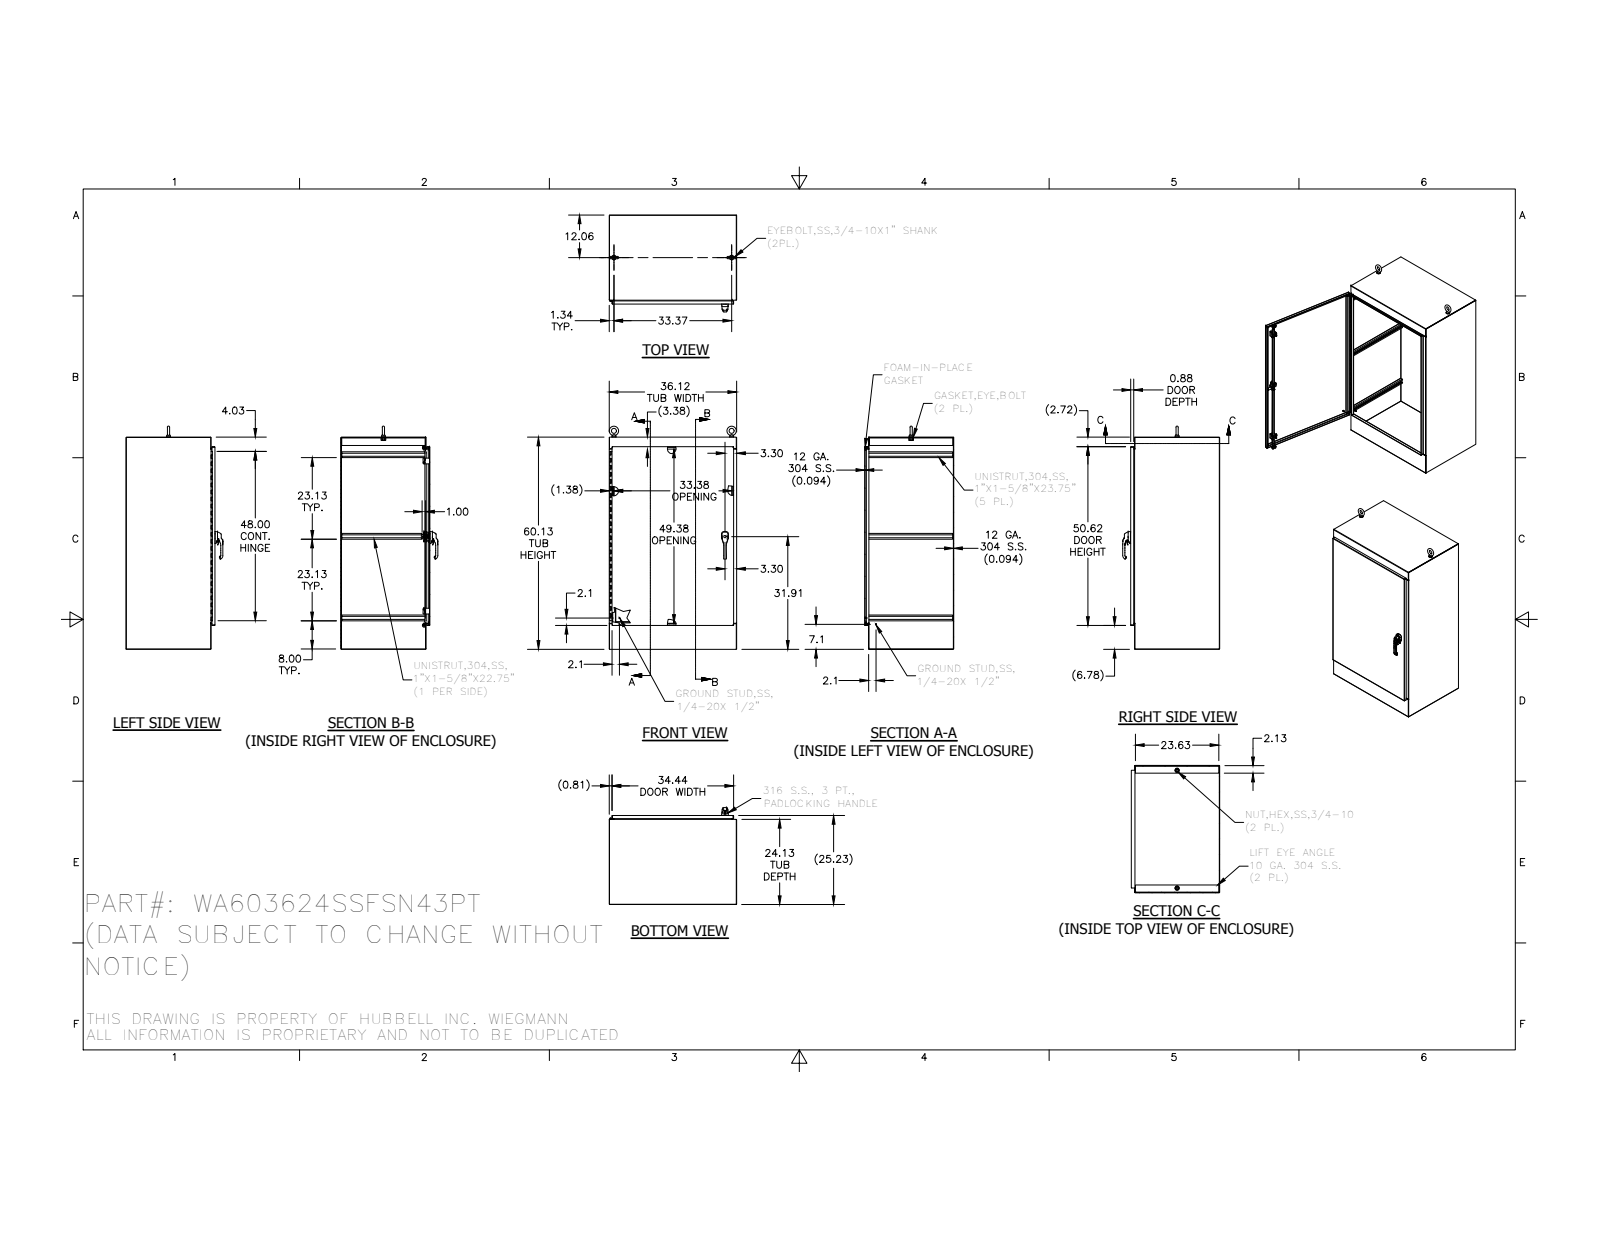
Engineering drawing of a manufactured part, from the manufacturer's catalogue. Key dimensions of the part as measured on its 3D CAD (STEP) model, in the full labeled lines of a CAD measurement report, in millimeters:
Part name (STEP PRODUCT): HFW369101; 37028; FUN00132_23.75(_DQ); 1091-BR11_AF0 (+8 more)
STEP written by: SolidWorks 2014 (AUTOMOTIVE_DESIGN)
Units: millimetres
Bodies: 66 solids, 3391 faces (1174 planar, 1277 cylindrical, 940 other)
Overall size (bounding box): 1606.5 × 917.6 × 697.9
Volume: 16 880 000 mm³ · Surface area: 13 730 000 mm²
Round holes (diameter × count): ⌀6.7 ×8, ⌀9.5 ×8, ⌀4.7 ×4, ⌀5.4 ×3, ⌀6.4 ×3, ⌀7.1 ×3, ⌀4.2 ×2, ⌀6.1 ×2, ⌀6.4 ×2, ⌀8 ×2, ⌀10.2 ×2, ⌀10.2 ×2
Round bosses / shafts (diameter × count): ⌀25.4 ×3, ⌀6 ×3, ⌀31.8 ×2, ⌀28.4 ×2, ⌀19.1 ×2, ⌀14.3 ×2, ⌀13.5 ×2, ⌀13.5 ×2
Partial cylindrical surfaces — rounded edges, fillets, slot ends (radius × count): R0.5 ×178, R0.3 ×106, R3.2 ×26, R0.5 ×23, R1.3 ×19, R0.8 ×17, R2 ×14, R3.2 ×13
Main face-to-face distances: 2.4, 638.4, 915.2, 636, 640.8, 1524.8, 912.8, 917.6, 610.4, 28
Hole centre spacings: 406.4, 9.7, 19.3, 28, 43.5, 70.2, 135.5, 270.9
